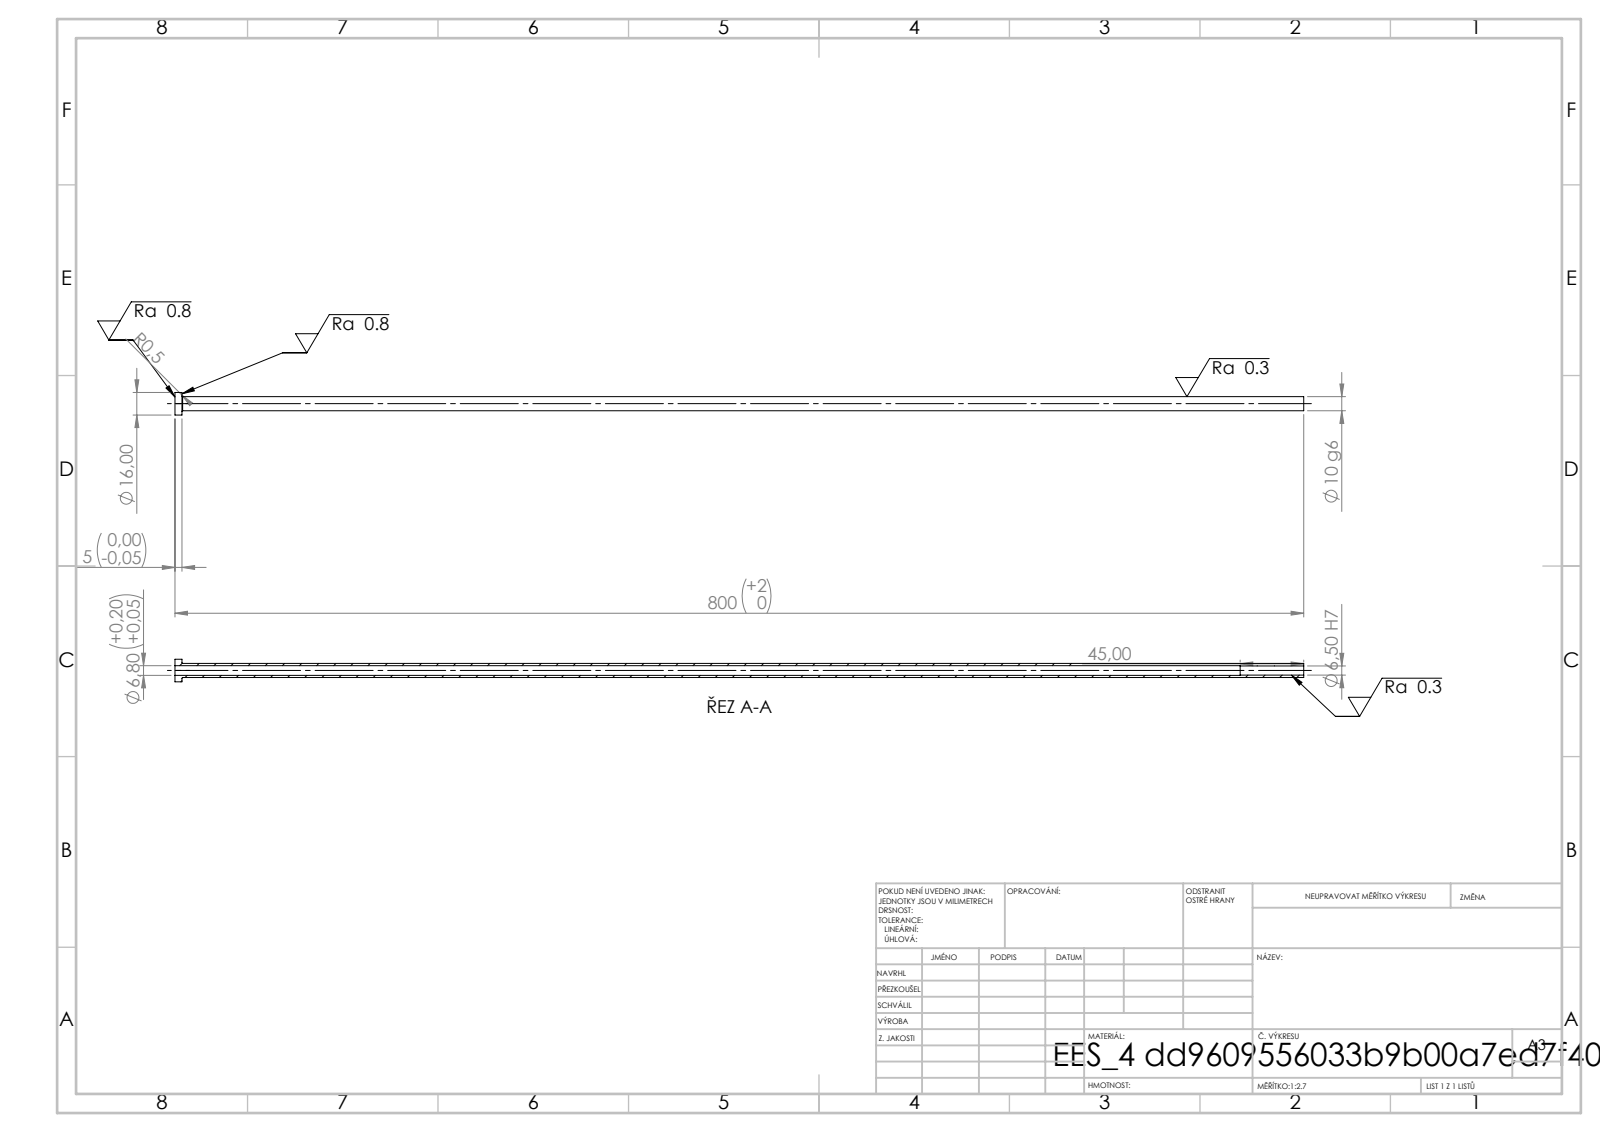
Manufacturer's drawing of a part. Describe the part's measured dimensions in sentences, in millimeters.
Its 3-D file was written by "SolidWorks 2019 (CONFIG_CONTROL_DESIGN)". It is 1 solid with 14 faces: 4 planar, 8 cylindrical and 2 other. Overall it measures 800 by 16 by 16 millimeters. Its volume is 34 534 cubic millimeters and its surface area 42 604 square millimeters. Round holes: 1 of diameter 6.5, 1 of diameter 6.8. Round bosses or shafts: 1 of diameter 16, 1 of diameter 10. The main face-to-face distances are 5, 800, 795, 755, 750, 45.
